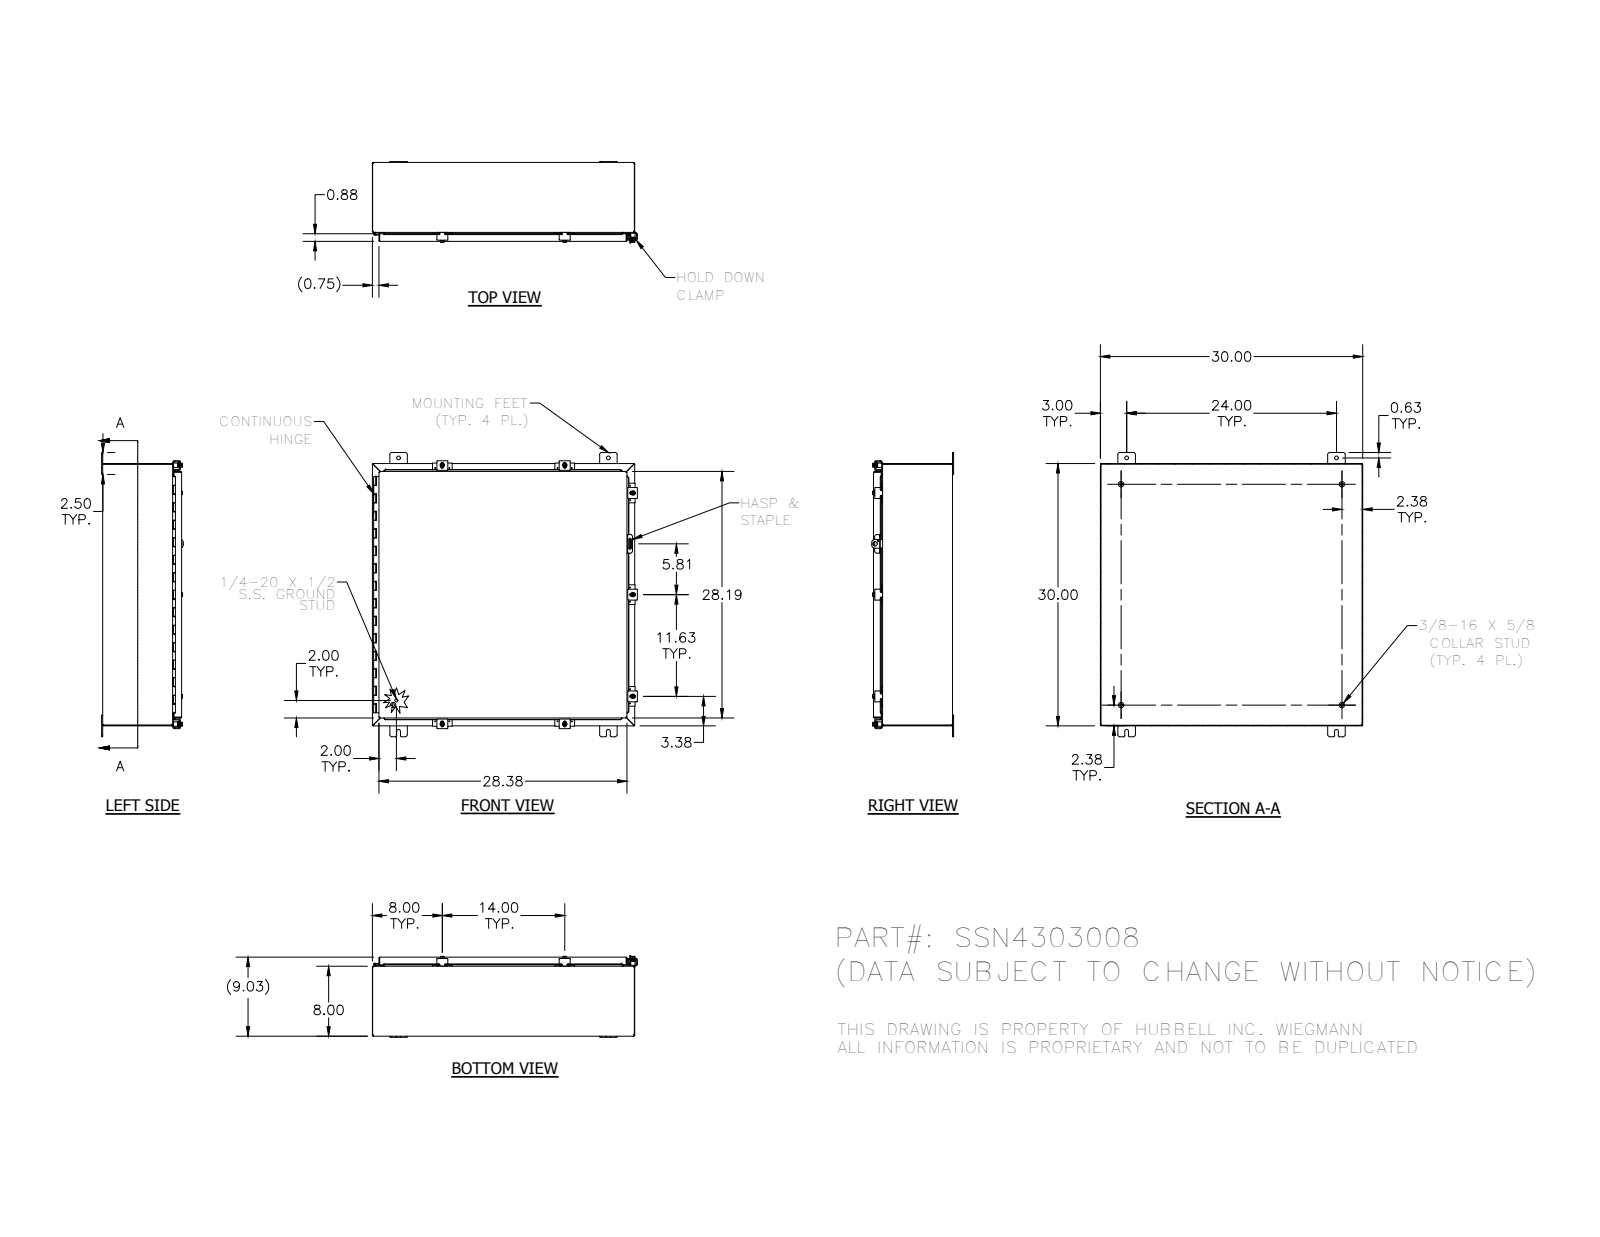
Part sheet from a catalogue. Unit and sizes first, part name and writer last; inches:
Units: inches
Overall size (bounding box): 32.5 × 30.311 × 9.355
Round holes (diameter × count): ⌀0.11 ×14, ⌀0.211 ×7, ⌀0.281 ×7, ⌀0.3 ×7, ⌀0.438 ×4, ⌀0.125 ×1, ⌀0.156 ×1, ⌀0.5 ×1
Round bosses / shafts (diameter × count): ⌀0.25 ×9, ⌀0.52 ×7, ⌀0.5 ×7, ⌀0.35 ×7, ⌀0.625 ×4, ⌀0.33 ×4, ⌀0.115 ×2, ⌀0.337 ×1
Partial cylindrical surfaces — rounded edges, fillets, slot ends (radius × count): R0.03 ×83, R0.125 ×37, R0.25 ×33, R0.031 ×23, R0.105 ×23, R0.062 ×15, R0.141 ×14, R0.1 ×10
Main face-to-face distances: 0.074, 8.959, 29.926, 8.885, 9.033, 29.852, 30, 7.926, 1.033, 8
Hole centre spacings: 0.876, 29.3, 14, 1.625, 13.191, 14.816, 28.961, 29.006
Volume: 245.1 in³ · Surface area: 6 451 in²
Bodies: 52 solids, 2111 faces (805 planar, 935 cylindrical, 371 other)
Part name (STEP PRODUCT): HFW30825-3; 328139P; 34871; 30818 (+8 more)
STEP written by: SolidWorks 2014 (AUTOMOTIVE_DESIGN)
